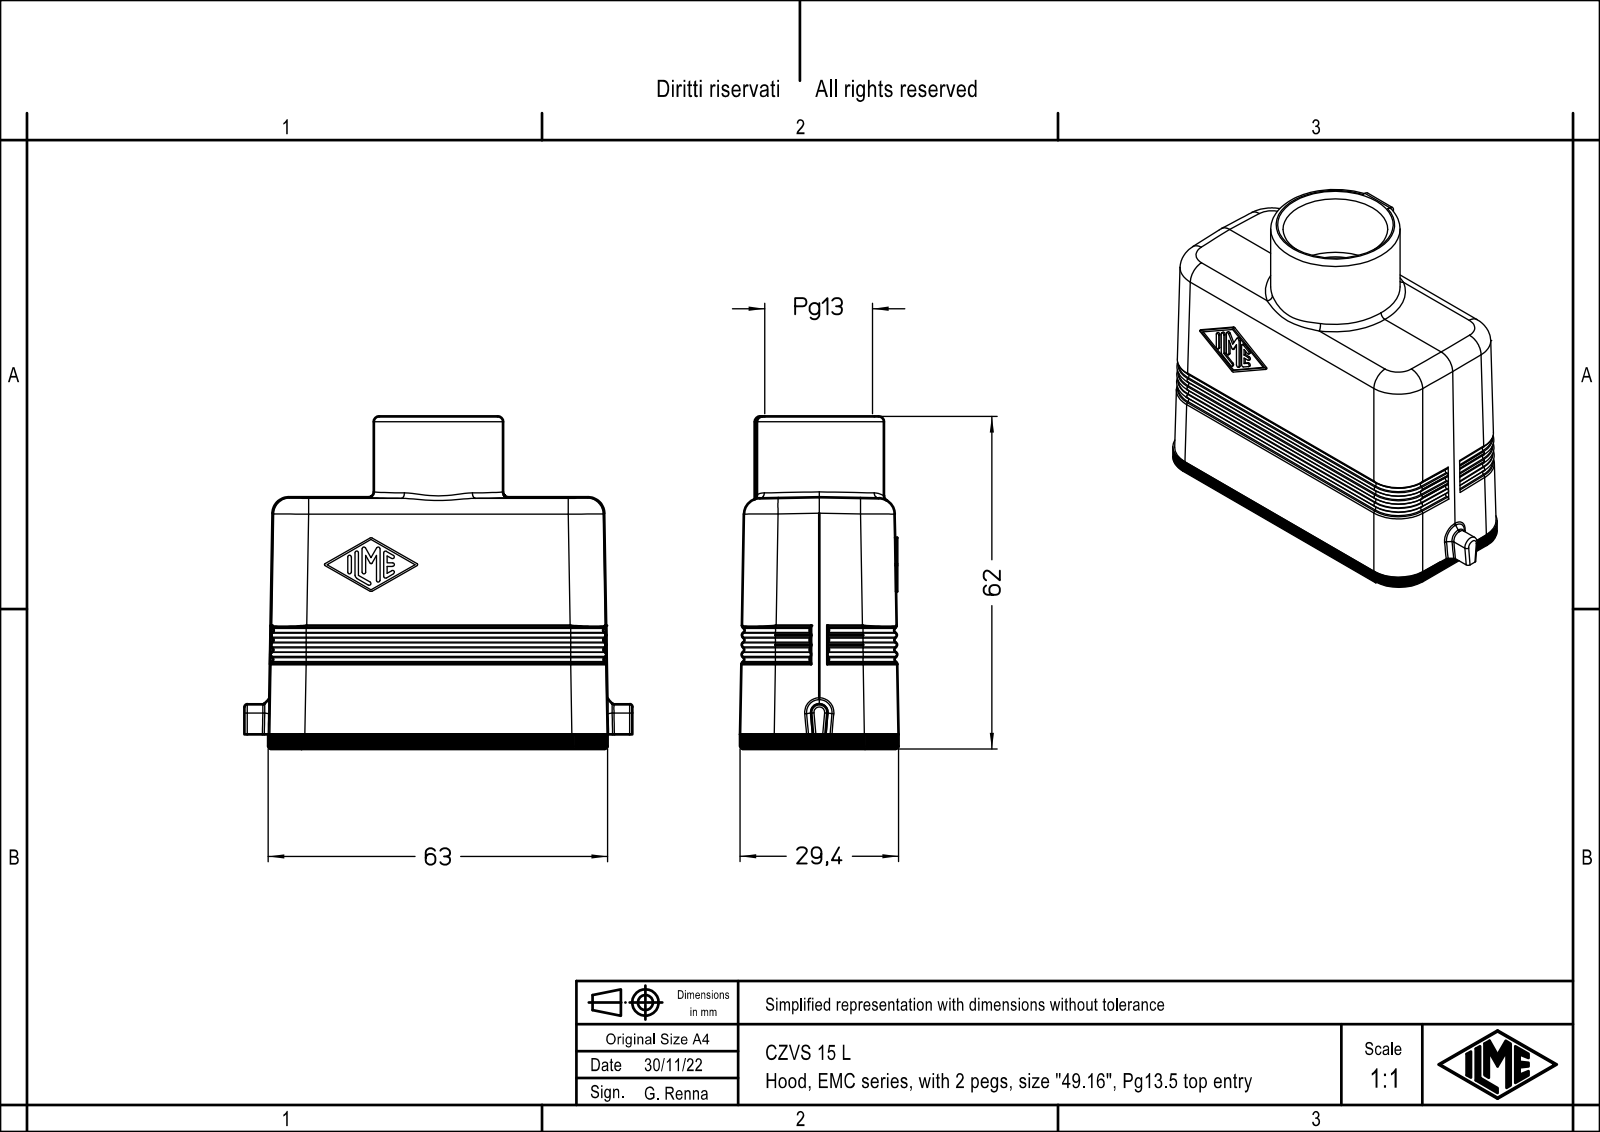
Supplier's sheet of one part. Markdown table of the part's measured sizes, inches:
| quantity | value |
| --- | --- |
| part name | CZ_MZ Tüllengehäuse 1 Bügel |
| STEP written by | Autodesk Inventor 7 (AUTOMOTIVE_DESIGN) |
| units | inches |
| bodies | 1 solid, 322 faces (153 planar, 86 cylindrical, 83 other) |
| overall size | 2.835 × 2.441 × 1.158 |
| volume | 2.206 in³ |
| surface area | 33.01 in² |
| round holes (diameter × count) | 0.097 × 4, 0.138 × 4, 0.672 × 1, 0.75 × 1 |
| round bosses / shafts (diameter × count) | 0.945 × 1, 0.142 × 1 |
| partial cylindrical surfaces (radius × count) | 0.01 × 14, 0.079 × 8, 0.157 × 8, 0.049 × 4, 0.13 × 2 |
| main face-to-face distances | 0.118, 1.039, 1.157, 0.921, 0.394, 2.087, 2.362, 1.969, 0.044, 2.48 |
| hole center spacings | 1.024, 0.63, 1.949, 2.048 |
